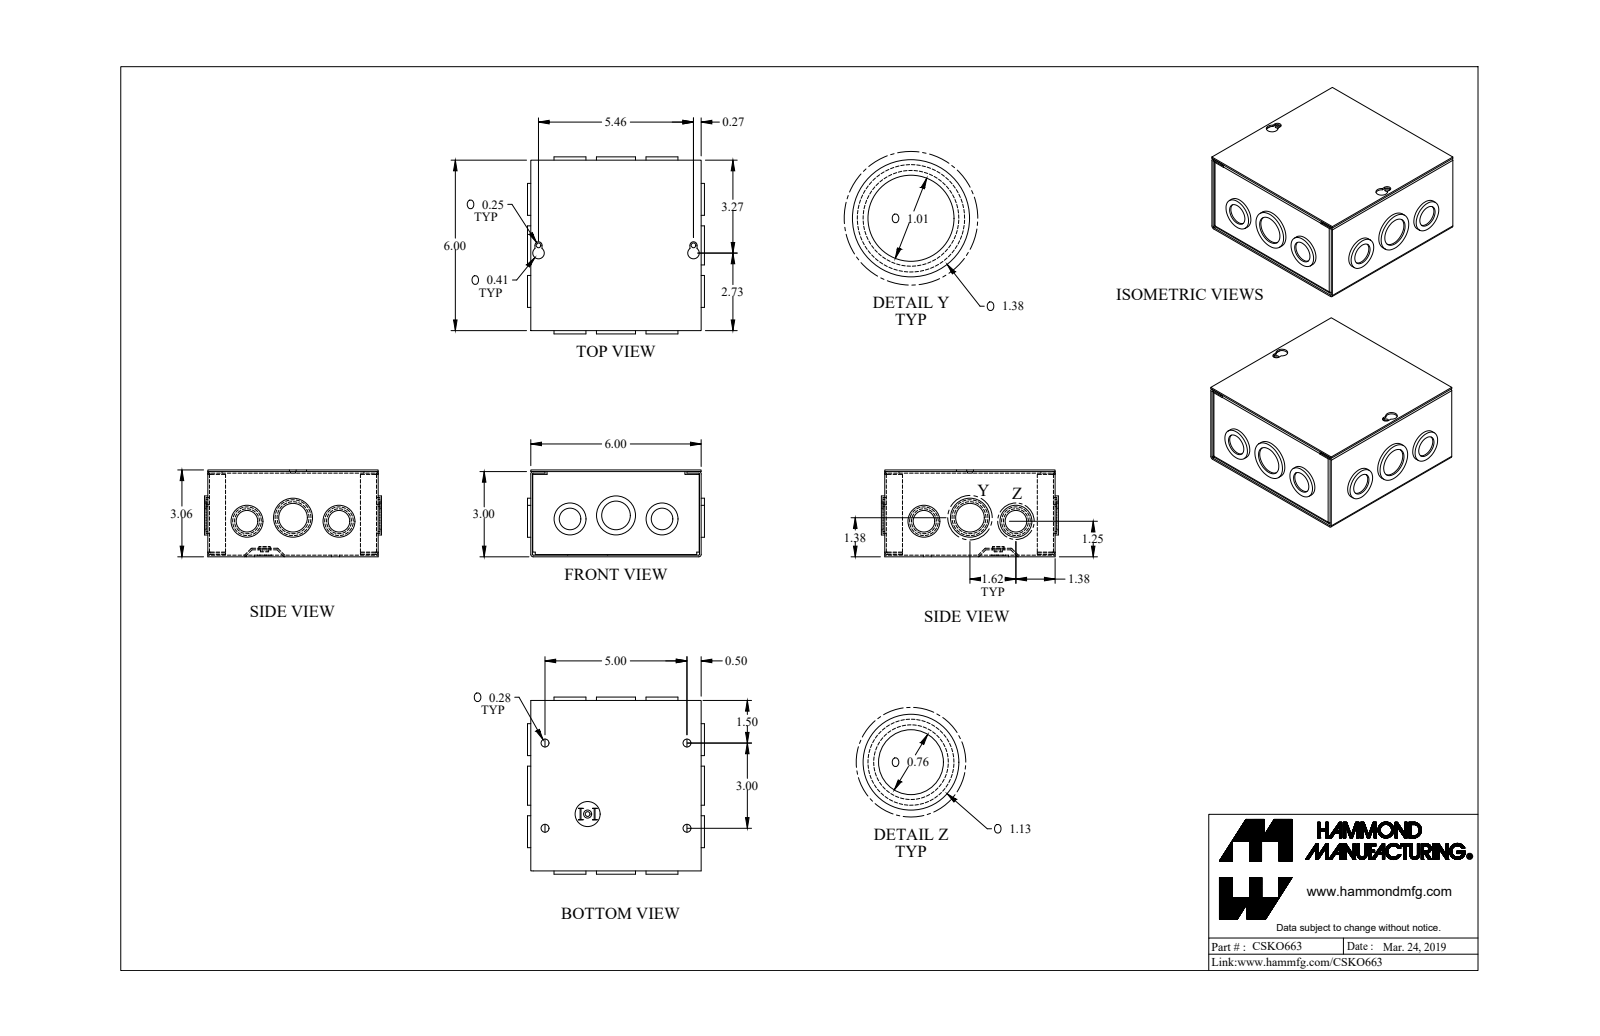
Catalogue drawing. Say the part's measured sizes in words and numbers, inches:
The part is named "CSKO663_Default". Its 3-D file was written by "SolidWorks 2019 (CONFIG_CONTROL_DESIGN)". It is 4 solids with 333 faces: 169 planar, 156 cylindrical and 8 other. Overall it measures 6.234 by 6.234 by 3.057 inches. Its volume is 9.64 cubic inches and its surface area 344.8 square inches. Round holes: 6 of diameter 1.011, 4 of diameter 0.281, 4 of diameter 0.761, 3 of diameter 0.17, 2 of diameter 1.261, 1 of diameter 0.5. Round bosses or shafts: 5 of diameter 1.125, 4 of diameter 0.875, 3 of diameter 0.875, 2 of diameter 1.375, 1 of diameter 1.125, 1 of diameter 0.492, 1 of diameter 0.284. Partial cylindrical surfaces (rounded edges, fillets, slot ends): 12 of radius 0.029, 12 of radius 0.086, 8 of radius 0.057, 2 of radius 0.125, 2 of radius 0.203. The main face-to-face distances are 0.057, 3, 5.943, 2.943, 6, 3.057, 5.886, 0.114, 0.08, 2.863. The hole center spacings are 1.517, 1.625, 5.441, 3, 3.24, 5, 5.831, 1.5.
